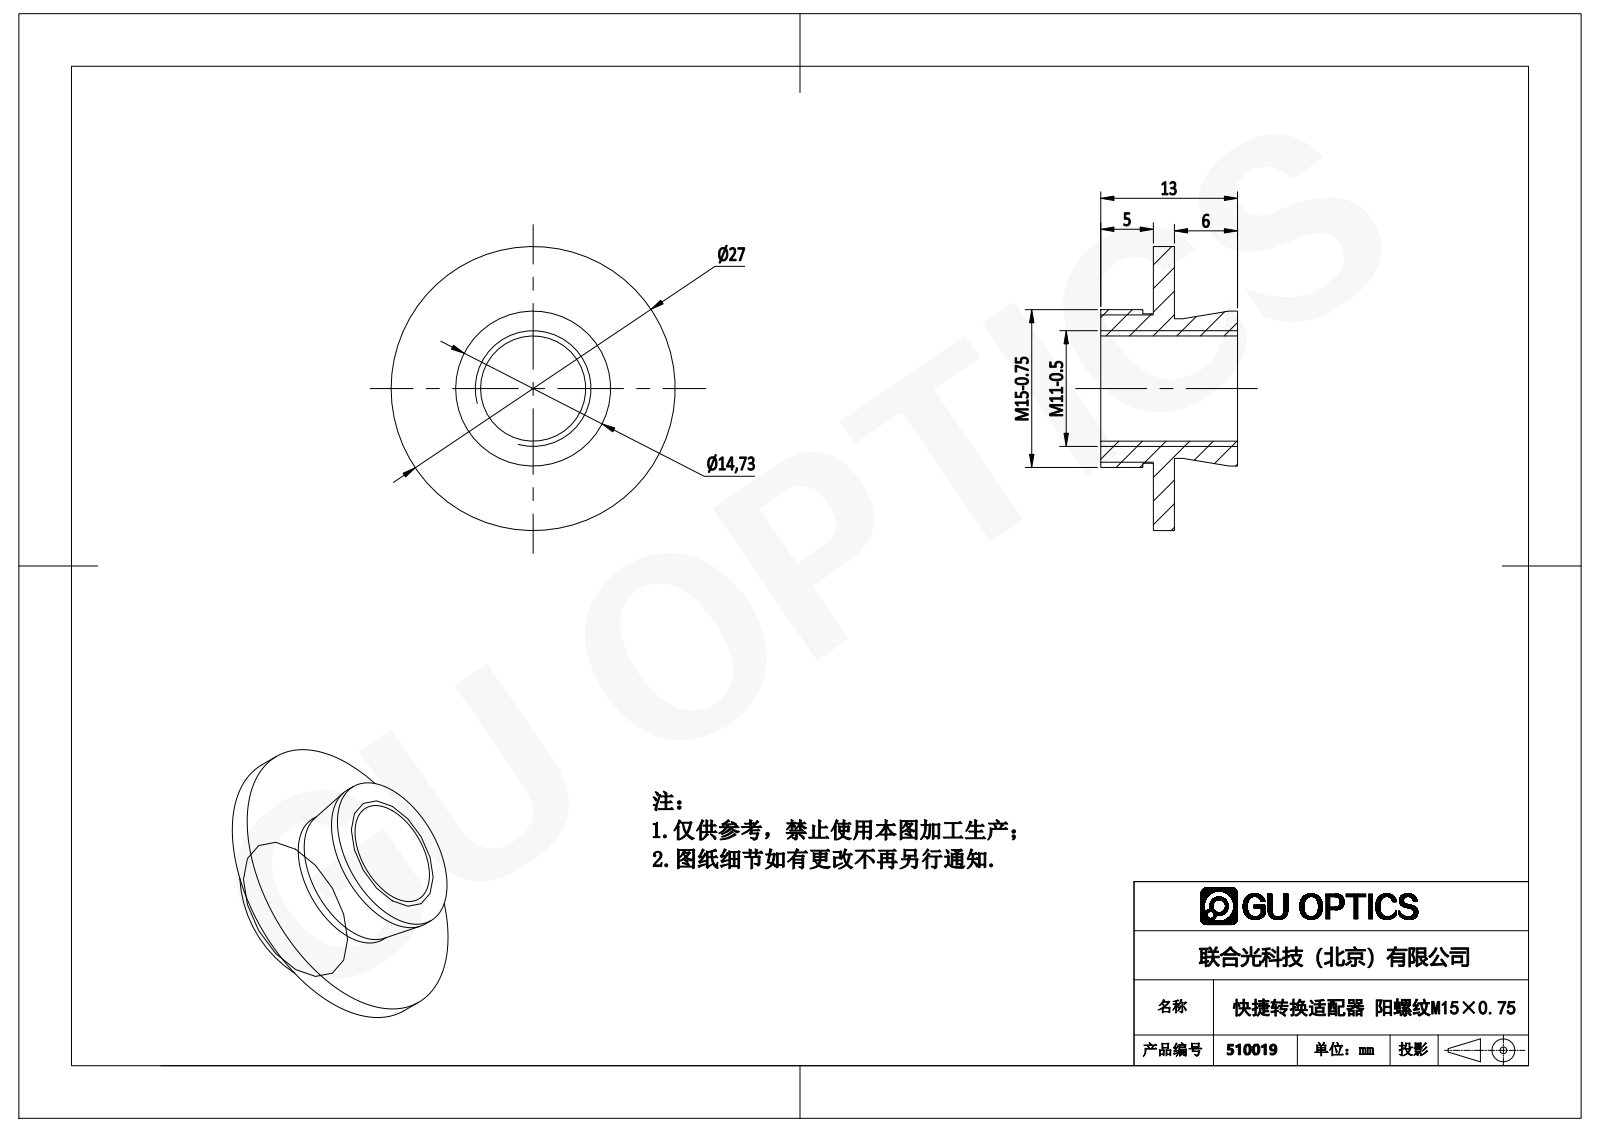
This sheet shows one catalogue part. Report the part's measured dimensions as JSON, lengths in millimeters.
{"part_name": "510019", "step_written_by": "SolidWorks 2016 (CONFIG_CONTROL_DESIGN)", "units": "millimeters", "bodies": {"solids": 1, "faces": 19, "planar": 5, "cylindrical": 12, "other": 2}, "overall_size": [27, 27, 13], "volume_mm3": 1914, "surface_area_mm2": 2135, "round_holes": [[10, 1]], "round_bosses_or_shafts": [[27, 1], [15, 1], [14.73, 1], [14.2, 1], [13.27, 1]], "face_to_face_distances": [2, 5, 7, 13, 8, 6, 4, 1, 3, 9]}
